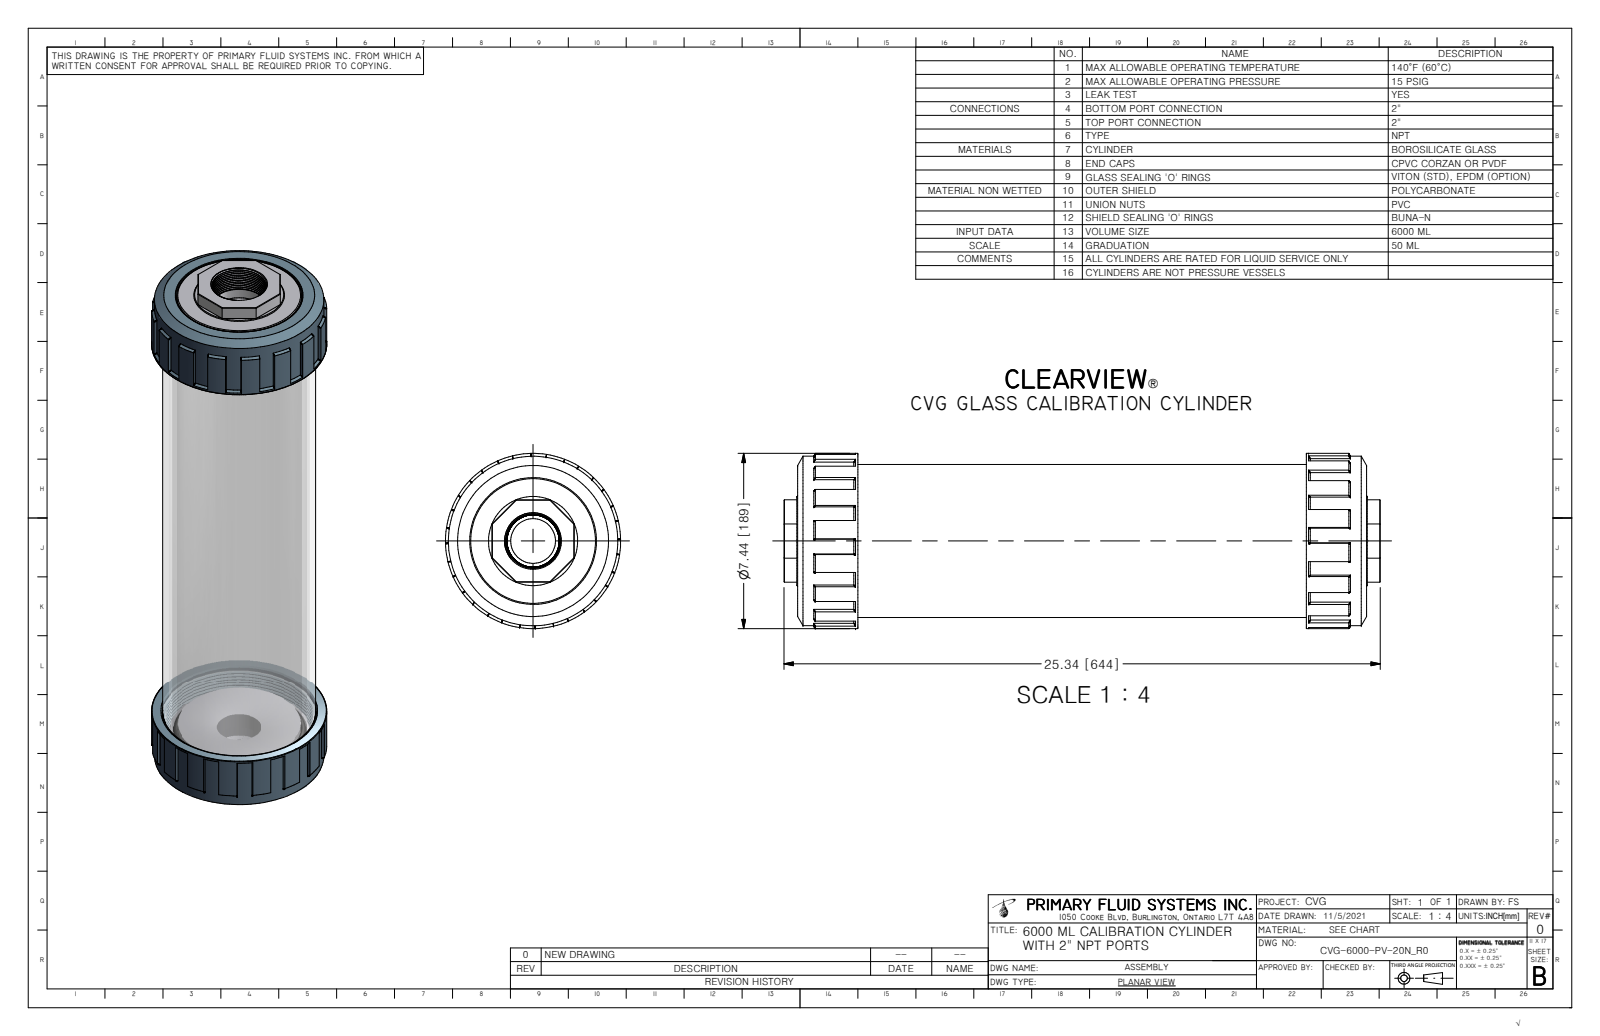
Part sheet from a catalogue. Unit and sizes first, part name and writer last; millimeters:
Units: millimetres
Overall size (bounding box): 643.6 × 189.1 × 189.1
Round holes (diameter × count): ⌀48.3 ×1, ⌀56.4 ×1, ⌀135 ×1, ⌀136.8 ×1, ⌀145 ×1, ⌀146.3 ×1, ⌀151.6 ×1, ⌀152.4 ×1, ⌀166 ×1
Round bosses / shafts (diameter × count): ⌀189.1 ×1, ⌀182.9 ×1, ⌀165.1 ×1, ⌀165 ×1, ⌀159 ×1, ⌀158.8 ×1, ⌀134.6 ×1, ⌀133 ×1
Partial cylindrical surfaces — rounded edges, fillets, slot ends (radius × count): R8.5 ×2, R85.9 ×2
Main face-to-face distances: 614.1, 65, 549.1, 14.7, 79.7, 563.9, 628.9, 484.1, 35.6, 608
Volume: 937 000 mm³ · Surface area: 1 474 000 mm²
Bodies: 1 solid, 361 faces (134 planar, 79 cylindrical, 148 other)
STEP written by: Autodesk Inventor 2009 (CONFIG_CONTROL_DESIGN)
